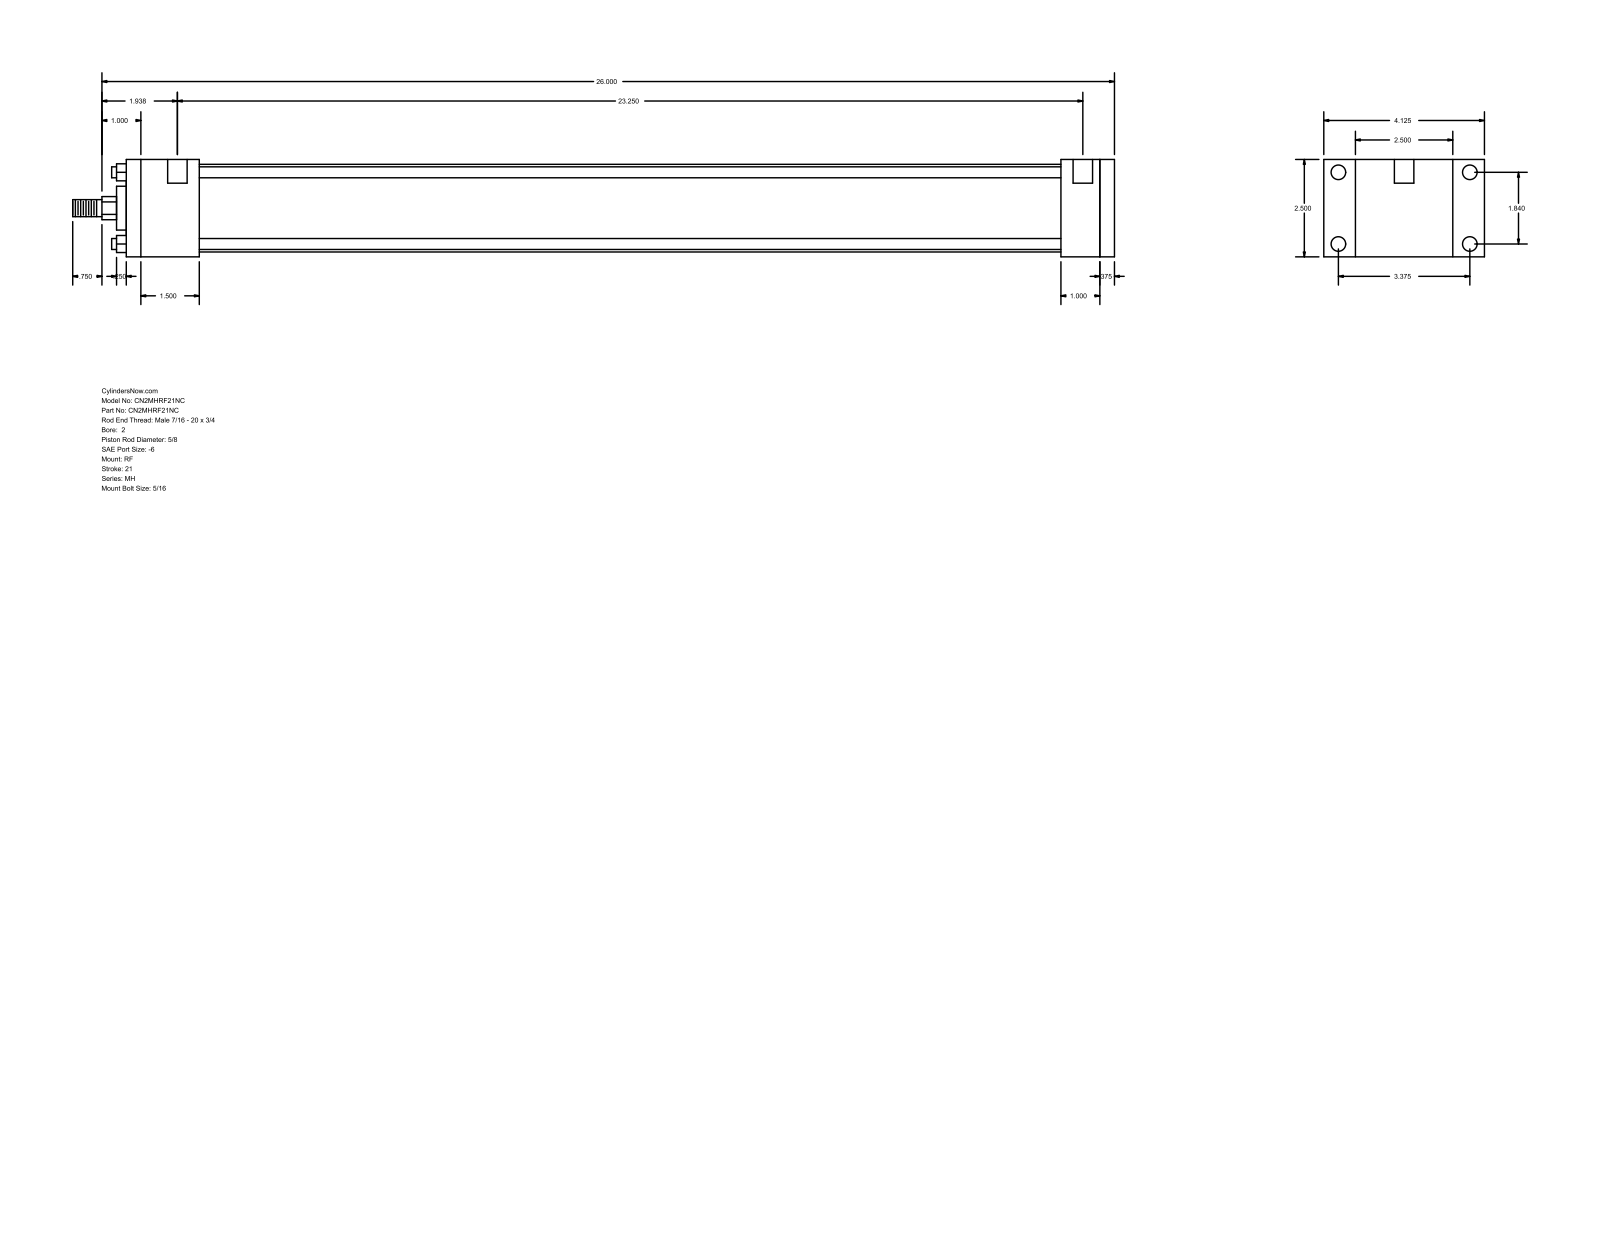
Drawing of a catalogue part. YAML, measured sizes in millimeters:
part_name: "MH_RF__0200_0.625"
step_written_by: "GSSL Pune (CONFIG_CONTROL_DESIGN)"
units: millimeters
bodies: {solids: 0, faces: 92, planar: 64, cylindrical: 28, other: 0}
overall_size: [679.45, 104.78, 63.5]
round_holes:
  - {diameter: 5.56, count: 4}
  - {diameter: 9.53, count: 4}
  - {diameter: 12.7, count: 2}
round_bosses_or_shafts:
  - {diameter: 7.14, count: 4}
  - {diameter: 57.15, count: 1}
  - {diameter: 28.57, count: 1}
  - {diameter: 15.88, count: 1}
  - {diameter: 11.11, count: 1}
partial_cylinders:
  - {radius: 7.54, count: 1}
face_to_face_distances: [63.5, 644.52, 635, 9.52, 25.4, 47.62, 609.6, 561.98, 587.38, 596.9]
hole_center_spacings: [46.74, 85.72, 97.63, 598.49, 3.18, 4.76, 590.55, 593.73]
